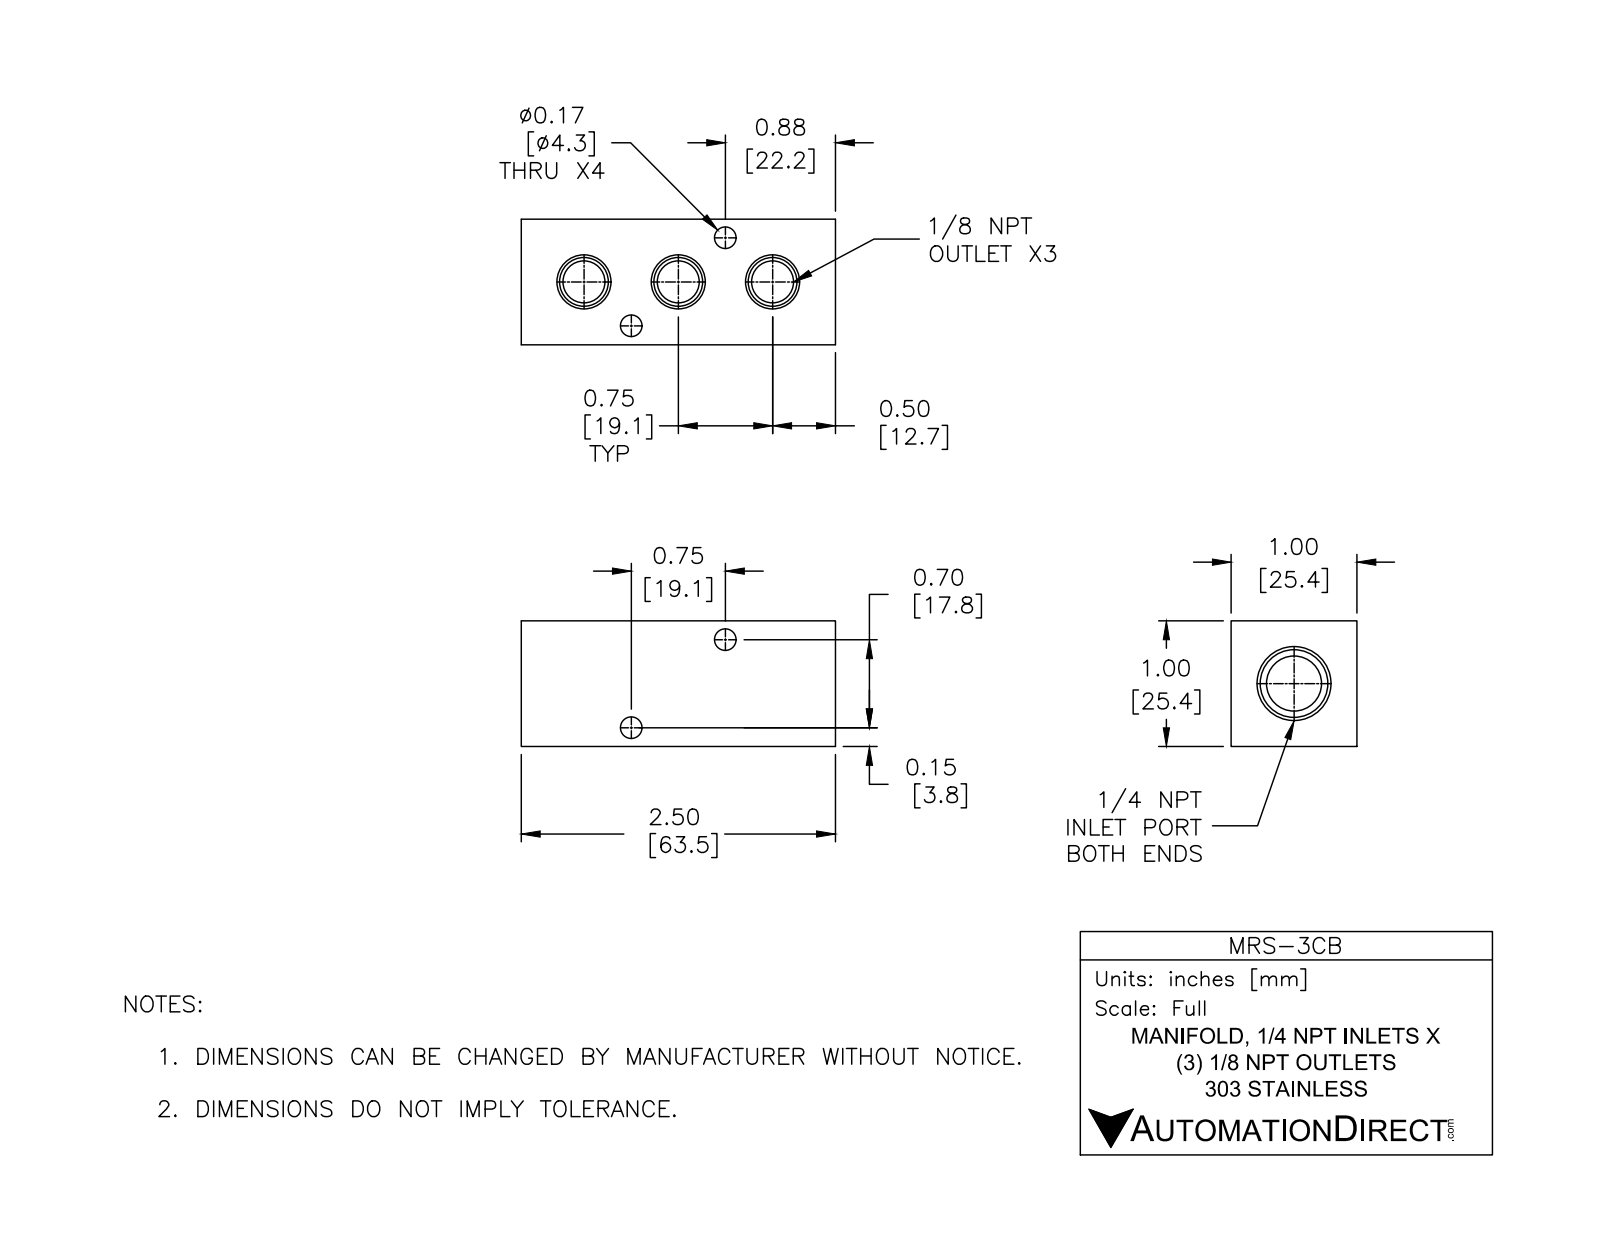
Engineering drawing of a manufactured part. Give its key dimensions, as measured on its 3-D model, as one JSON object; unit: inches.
{"part_name": "MRS-3CB", "step_written_by": "SolidWorks 2015 (CONFIG_CONTROL_DESIGN)", "units": "inches", "bodies": {"solids": 1, "faces": 54, "planar": 11, "cylindrical": 23, "other": 20}, "overall_size": [2.5, 1, 1], "volume_in3": 1.877, "surface_area_in2": 17.48, "round_holes": [[0.17, 4], [0.332, 1], [0.438, 1]], "partial_cylinders_radius": [[0.166, 2]], "face_to_face_distances": [1, 2.5, 0.39, 2.11, 0.73, 0.27, 1.72], "hole_center_spacings": [0.513, 1.026]}
